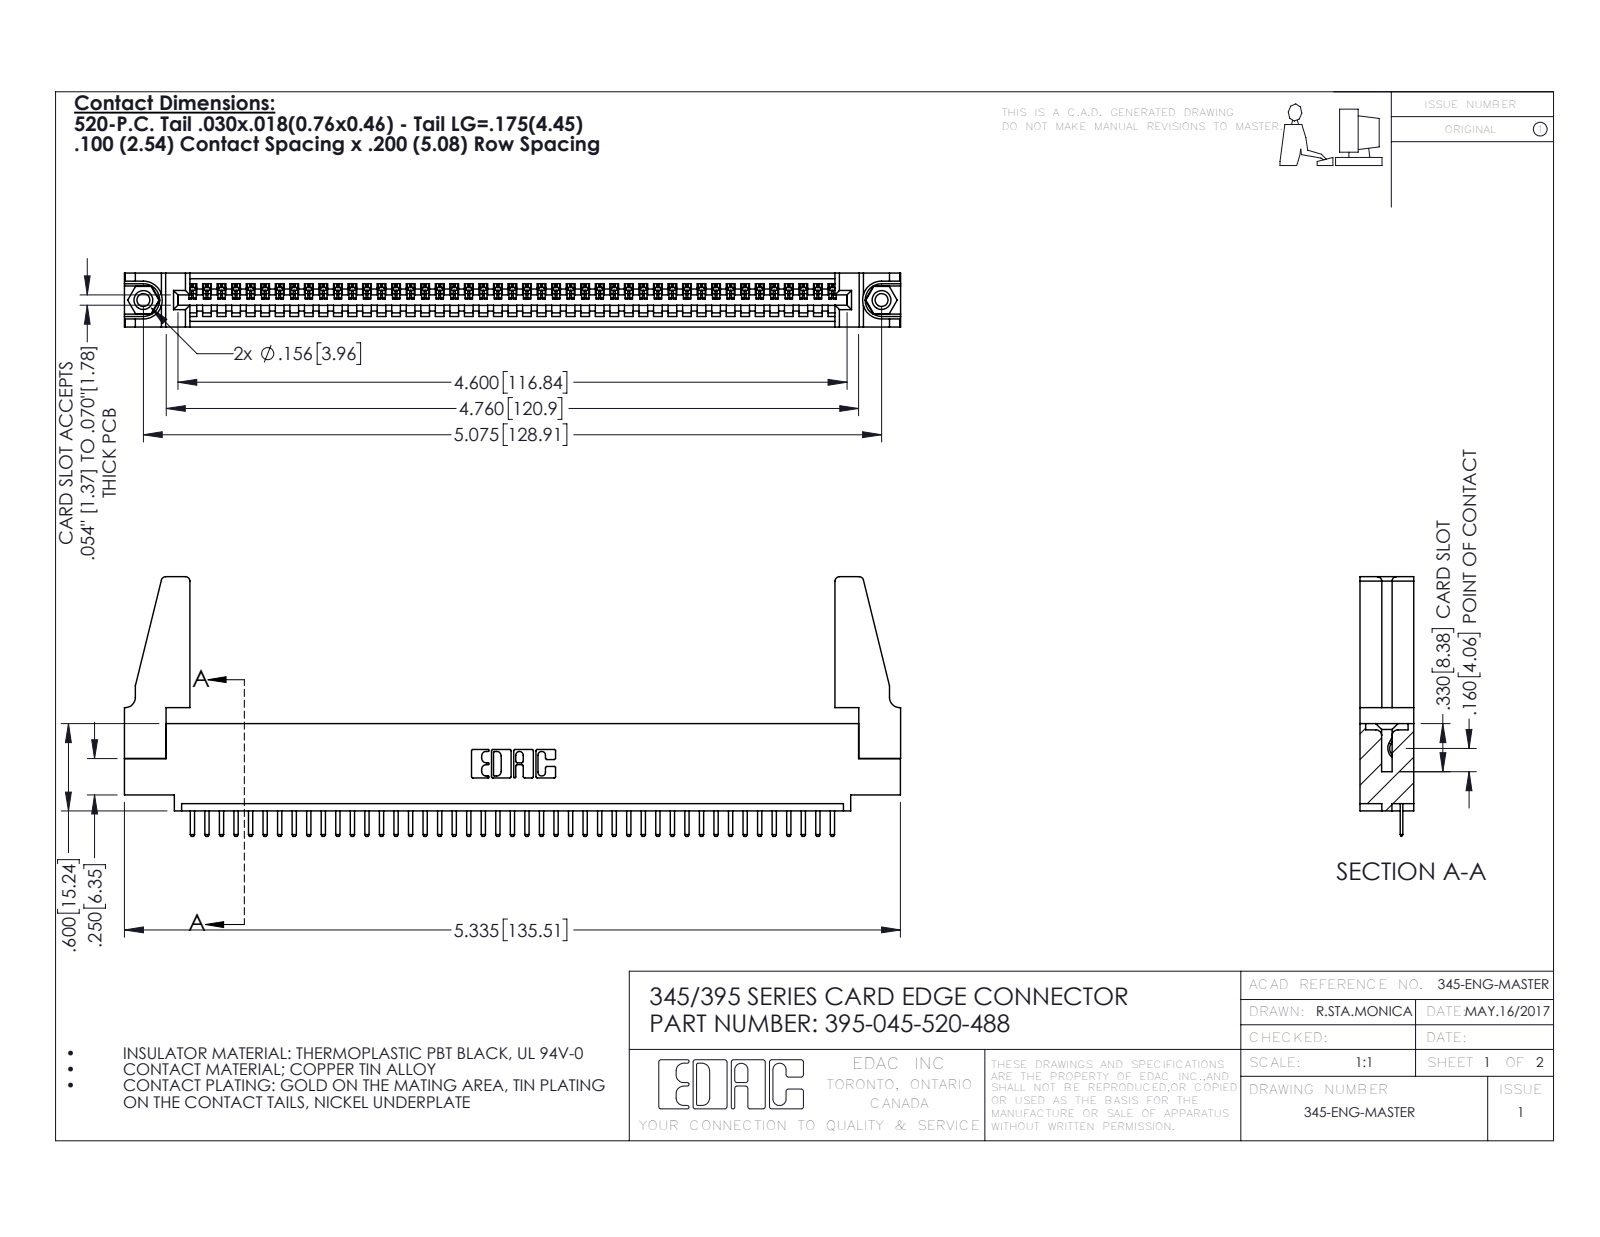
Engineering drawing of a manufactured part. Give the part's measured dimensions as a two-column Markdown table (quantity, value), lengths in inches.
| quantity | value |
| --- | --- |
| part name | 345-220-078_345-220-088; 345-250-001_345-250-001-102; 345 Part_0.110 Offset - 0.156 Dia-TH; 345-292-001_345-293-120 (+1 more) |
| STEP written by | SolidWorks 2016 (CONFIG_CONTROL_DESIGN) |
| units | inches |
| bodies | 50 solids, 3044 faces (2046 planar, 982 cylindrical, 16 other) |
| overall size | 5.336 × 1.785 × 0.37 |
| volume | 0.973 in³ |
| surface area | 30.53 in² |
| round holes (diameter × count) | 0.089 × 2, 0.125 × 2, 0.156 × 2, 0.064 × 1 |
| round bosses / shafts (diameter × count) | 0.155 × 2 |
| partial cylindrical surfaces (radius × count) | 0.01 × 92, 0.006 × 90, 0.01 × 22, 0.03 × 8, 0.007 × 6, 0.031 × 6, 0.026 × 3, 0.031 × 2 |
| main face-to-face distances | 0.072, 0.37, 0.298, 0.2, 0.098, 0.272, 0.025, 0.225, 0.072, 0.149 |
| hole center spacings | 0.27, 4.839, 5.075 |
